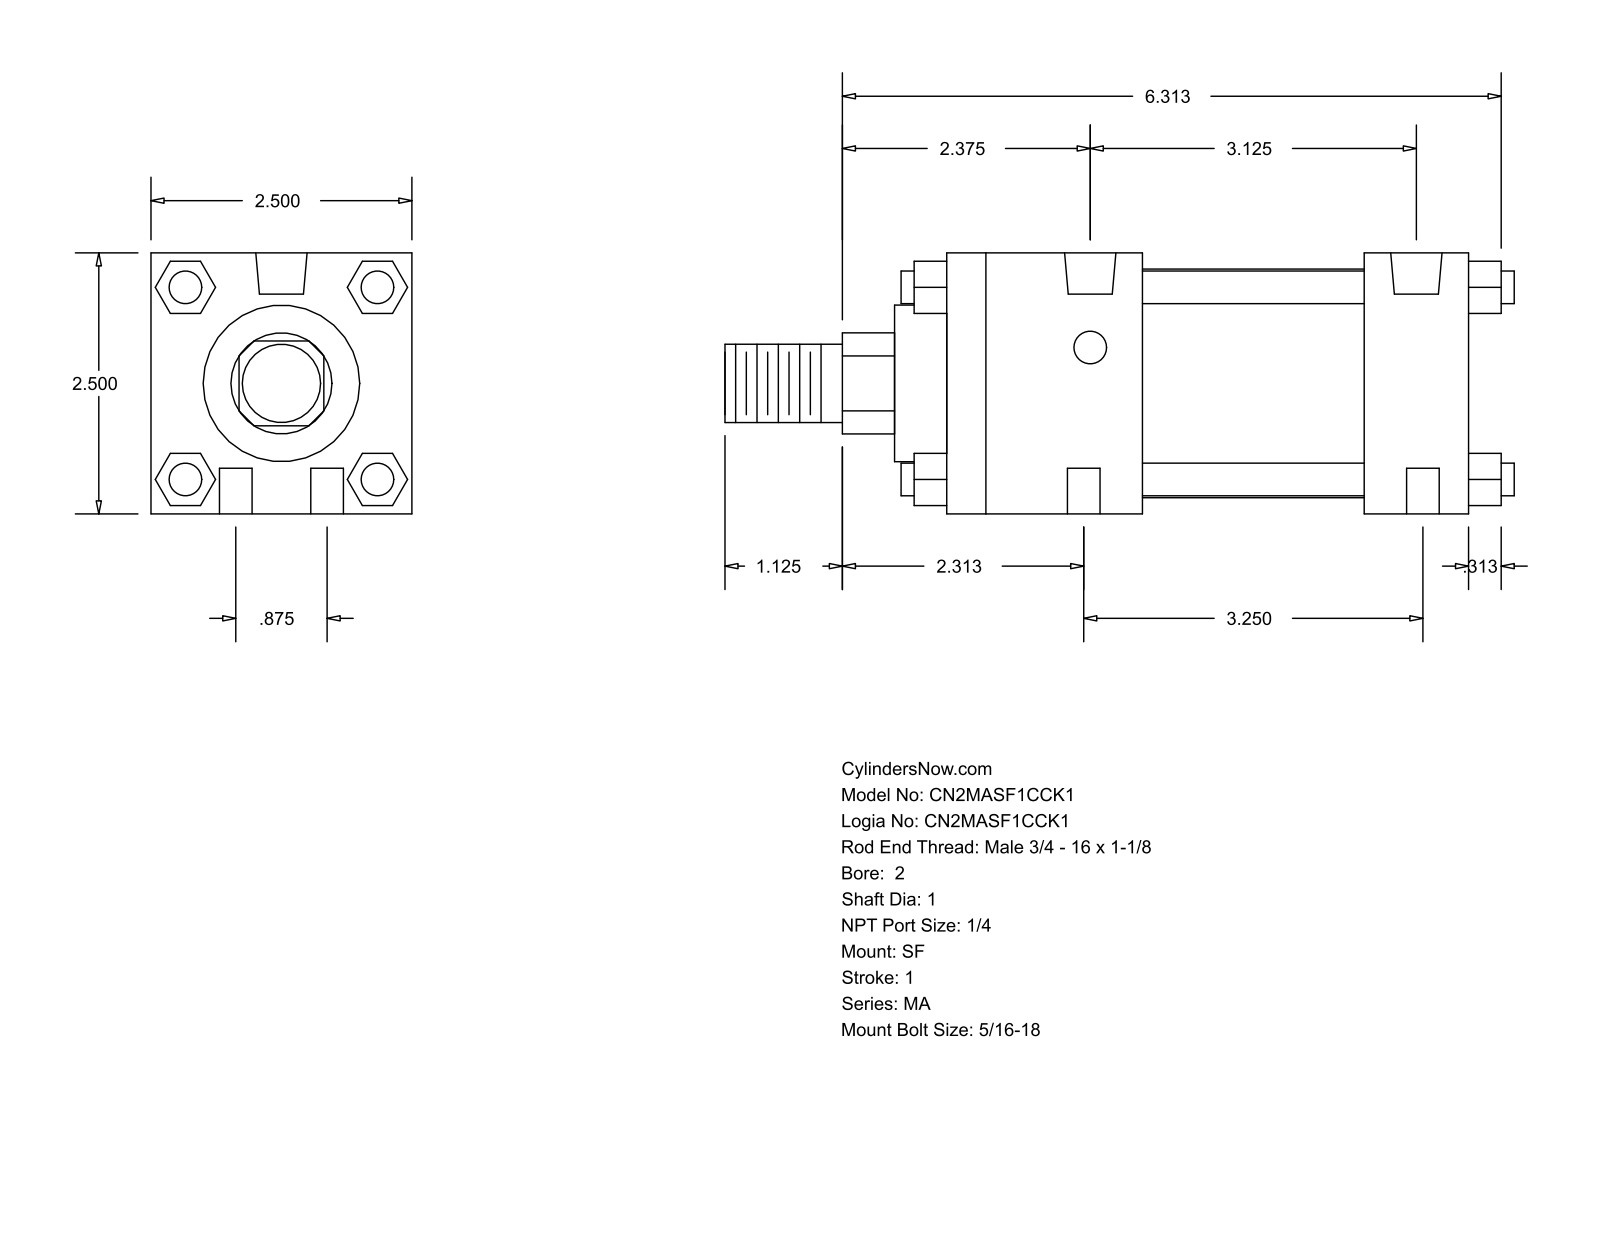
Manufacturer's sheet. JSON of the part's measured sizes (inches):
{"part_name": "MA_SF__0200_1", "step_written_by": "GSSL Pune (CONFIG_CONTROL_DESIGN)", "units": "inches", "bodies": {"solids": 0, "faces": 124, "planar": 94, "cylindrical": 30, "other": 0}, "overall_size": [7.563, 2.5, 2.5], "round_holes": [[0.313, 6], [0.492, 2]], "round_bosses_or_shafts": [[0.313, 4], [2.19, 1], [1.5, 1], [1, 1], [0.75, 1]], "partial_cylinders_radius": [[0.484, 1]], "face_to_face_distances": [2.5, 5, 0.5, 4, 2.125, 1, 1.875, 3.125, 1.593, 0.92], "hole_center_spacings": [0.442, 3.217, 0.875, 3.125, 3.25, 3.366]}
